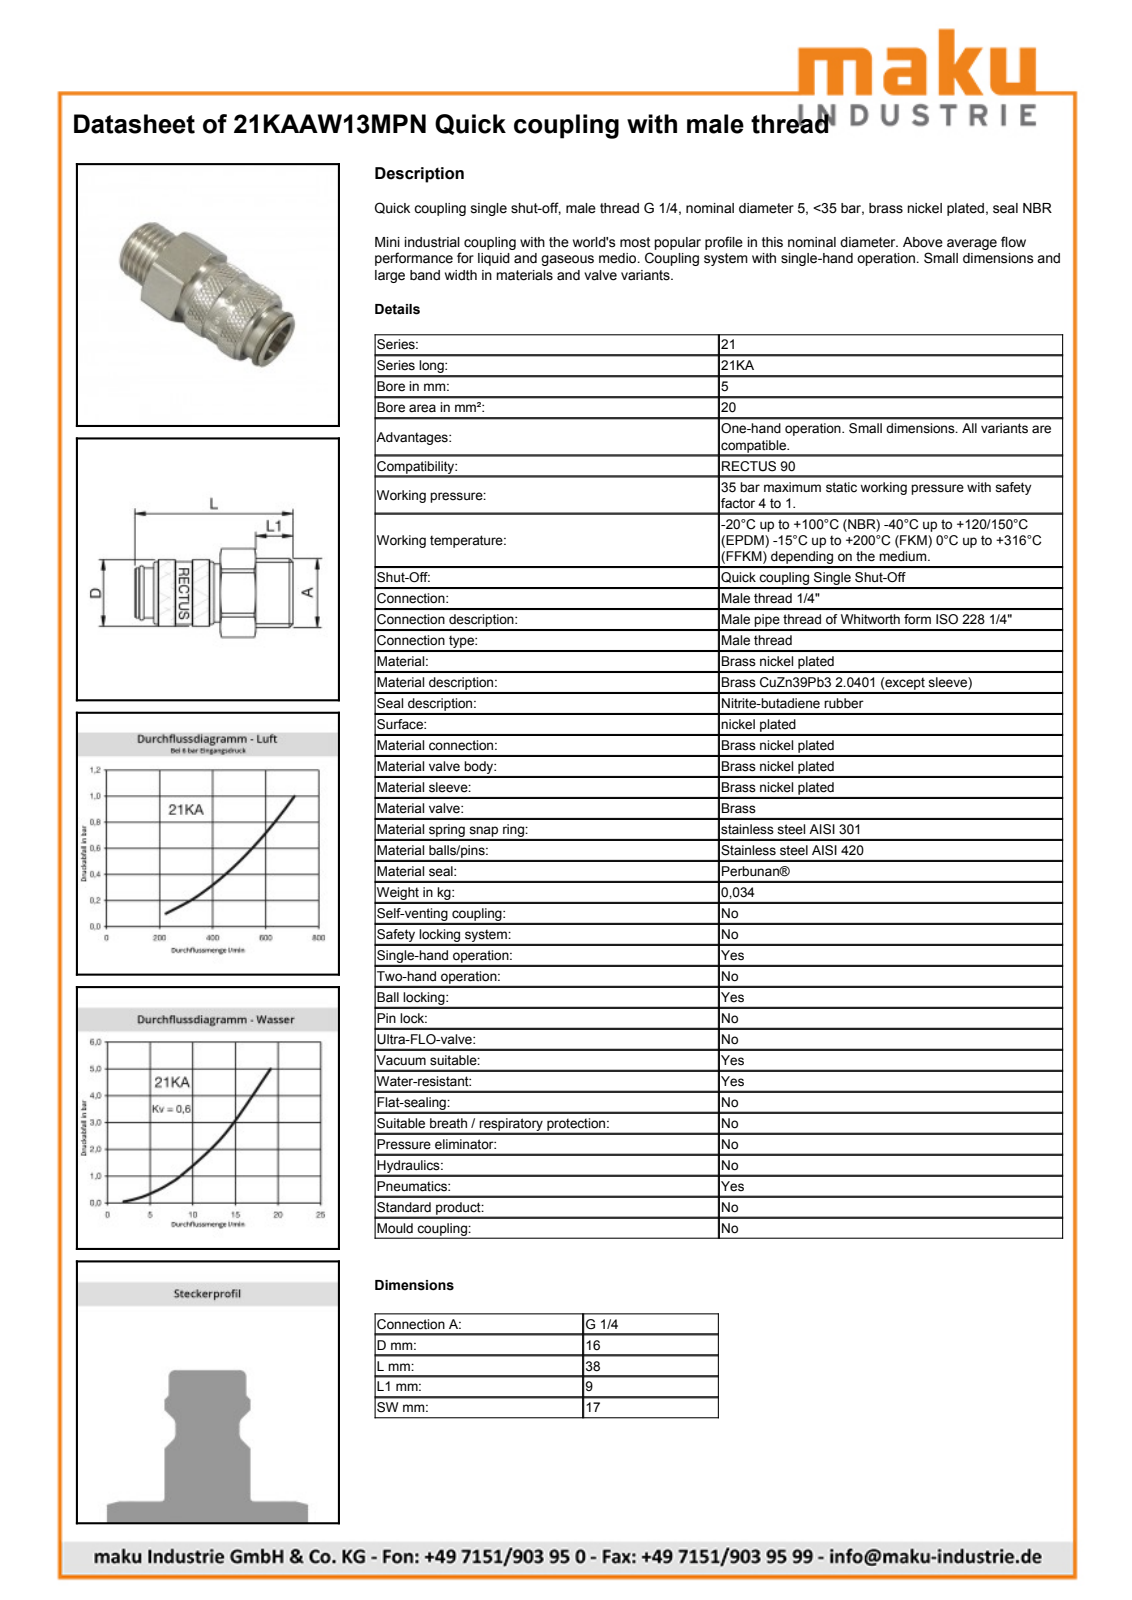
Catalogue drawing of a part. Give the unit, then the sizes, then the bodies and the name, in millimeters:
Units: millimetres
Overall size (bounding box): 38.06 × 19.15 × 17.13
Round holes (diameter × count): ⌀11.46 ×1, ⌀12.15 ×1, ⌀14 ×1
Round bosses / shafts (diameter × count): ⌀16.15 ×1, ⌀15.1 ×1, ⌀13.16 ×1, ⌀12 ×1, ⌀11.4 ×1, ⌀11.15 ×1
Partial cylindrical surfaces — rounded edges, fillets, slot ends (radius × count): R5.63 ×1, R7.45 ×1, R9.57 ×1
Main face-to-face distances: 17, 38.06, 29.06, 9, 20.51, 8.55, 17.55, 16.06, 4.45, 13
Volume: 6 582 mm³ · Surface area: 3 719 mm²
Bodies: 2 solids, 454 faces (149 planar, 61 cylindrical, 244 other)
Part name (STEP PRODUCT): D104698
STEP written by: Autodesk Inventor 2011 (AUTOMOTIVE_DESIGN)
